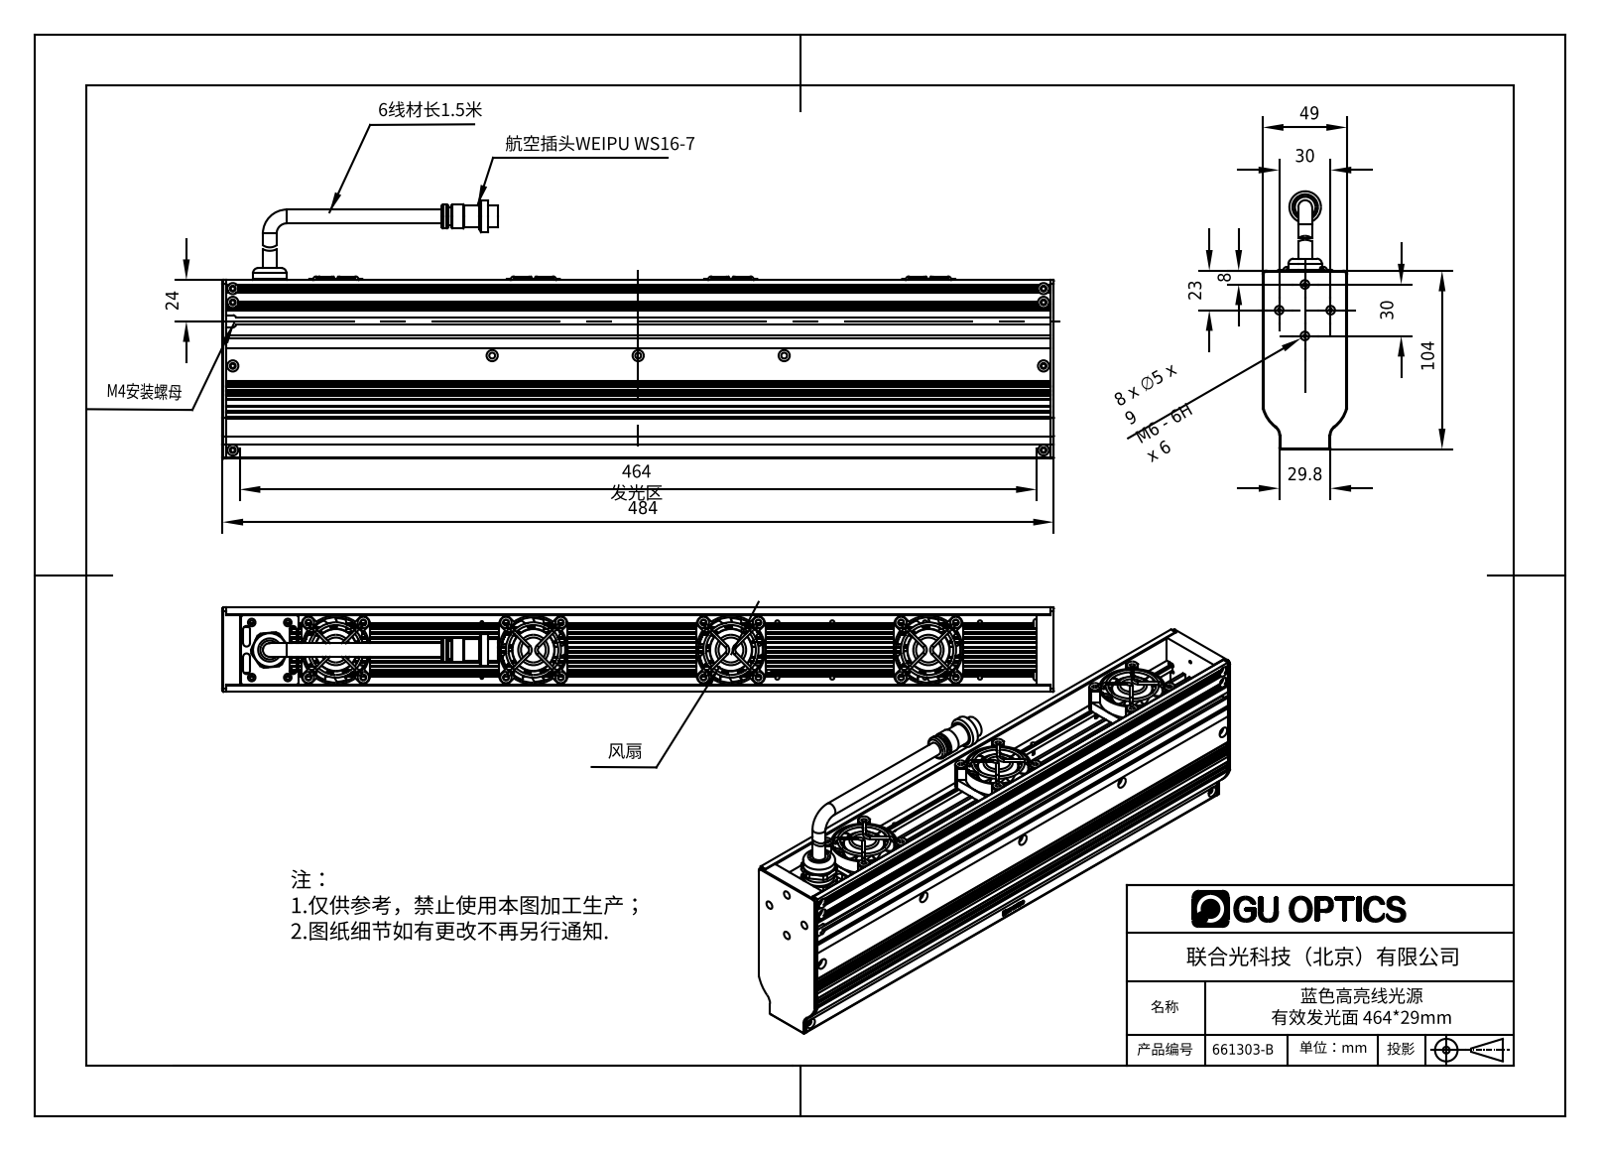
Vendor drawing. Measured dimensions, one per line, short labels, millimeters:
name: 661303-B
written by: SolidWorks 2016 (AUTOMOTIVE_DESIGN)
unit: mm
bodies: 26 solids, 2231 faces (924 planar, 693 cylindrical, 614 other)
size: 356 × 150.2 × 49
volume: 895 739 mm³; area: 432 227 mm²
holes: 25× ⌀2.5, 12× ⌀3.2, 12× ⌀6.2, 11× ⌀3.4, 10× ⌀1.6, 10× ⌀3.5, 9× ⌀6.5, 6× ⌀1, 4× ⌀2.4, 4× ⌀5, 3× ⌀38, 1× ⌀11
bosses: 12× ⌀1.6, 3× ⌀24.8, 3× ⌀24, 3× ⌀2, 2× ⌀8, 1× ⌀35, 1× ⌀19.5, 1× ⌀19
rounds: 58× R1, 28× R0.2, 20× R2, 13× R5.1, 12× R0.4, 10× R0.5, 7× R3, 6× R1.11
face distances: 5.5, 2, 5, 1.7, 11, 5.1, 43.9, 7.2, 48.9, 43.8
hole spacings: 32, 3.5, 31.82, 45, 86, 26.8, 70, 3.51
